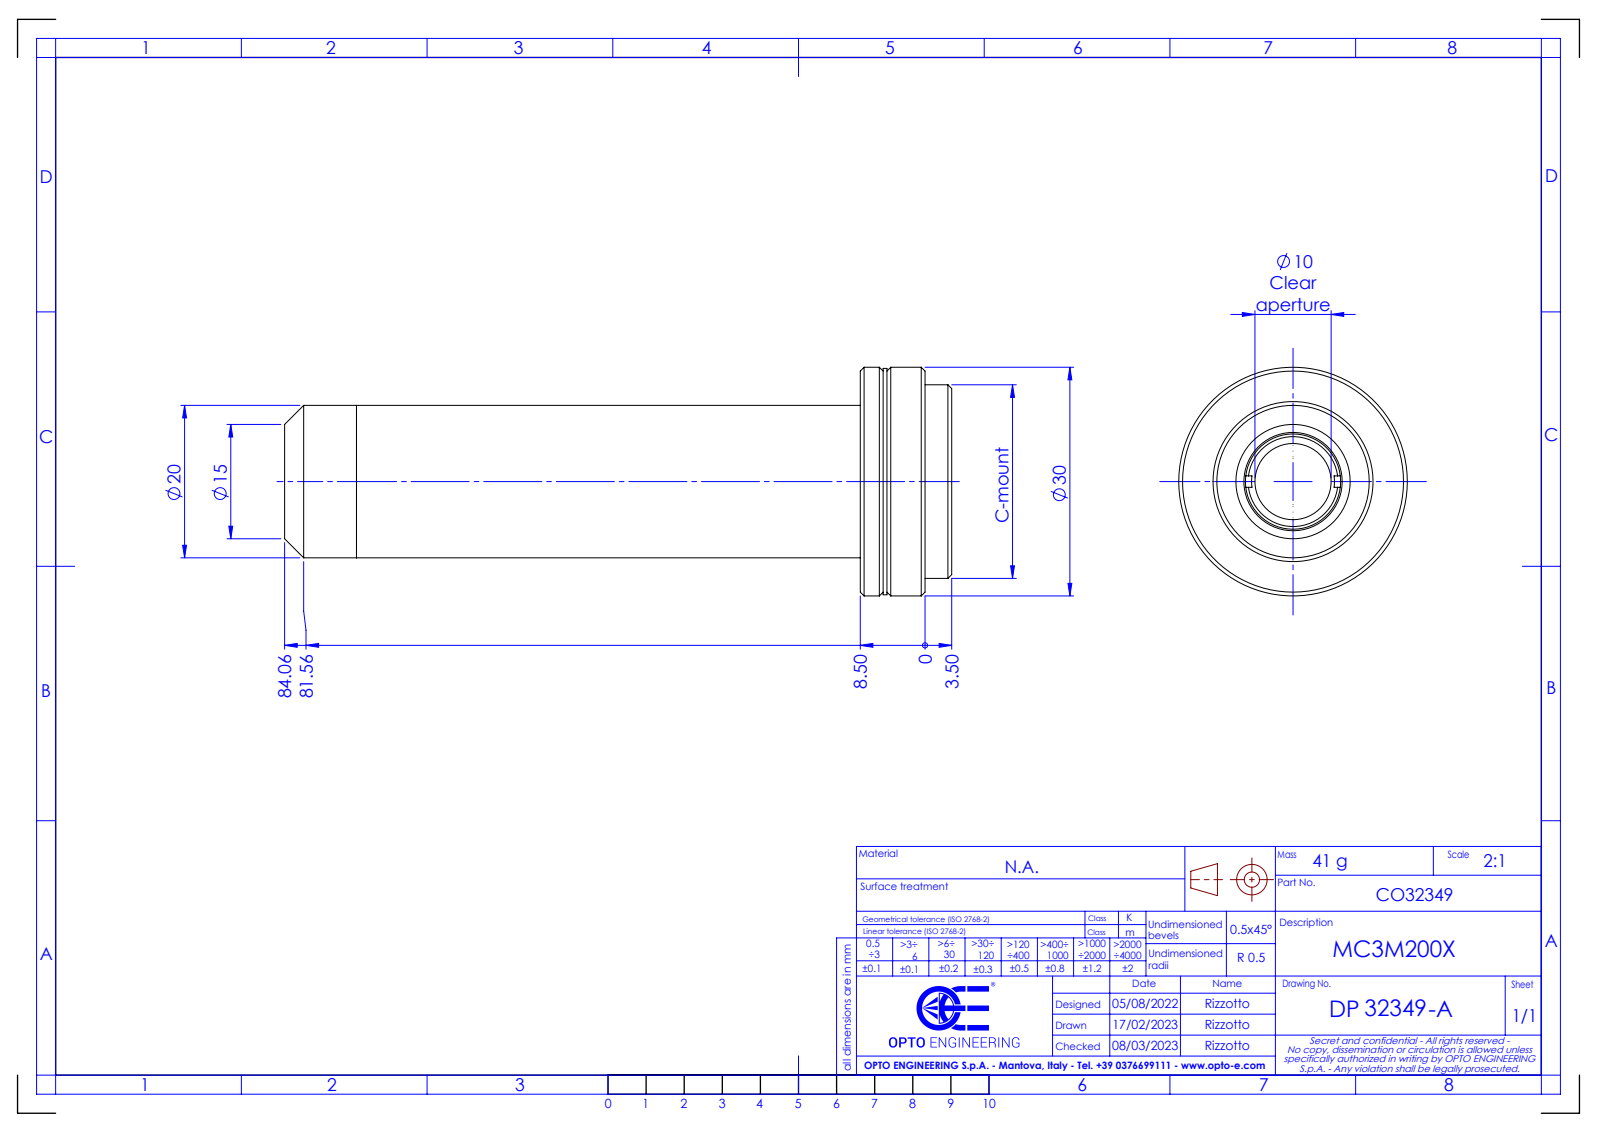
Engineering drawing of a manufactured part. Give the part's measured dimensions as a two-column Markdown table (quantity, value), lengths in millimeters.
| quantity | value |
| --- | --- |
| part name | DP32349-A_MC3M200X |
| STEP written by | SolidWorks 2021 (CONFIG_CONTROL_DESIGN) |
| units | millimeters |
| bodies | 0 solids, 64 faces (16 planar, 22 cylindrical, 26 other) |
| overall size | 87.56 × 30 × 30 |
| round holes (diameter × count) | 10 × 1, 12.5 × 1, 17.5 × 1, 18 × 1 |
| round bosses / shafts (diameter × count) | 30 × 1, 29.7 × 1, 25.4 × 1, 20 × 1 |
| main face-to-face distances | 8.5, 3.5, 5, 3, 0.5, 5.5, 12, 9, 66.13, 69.13 |
